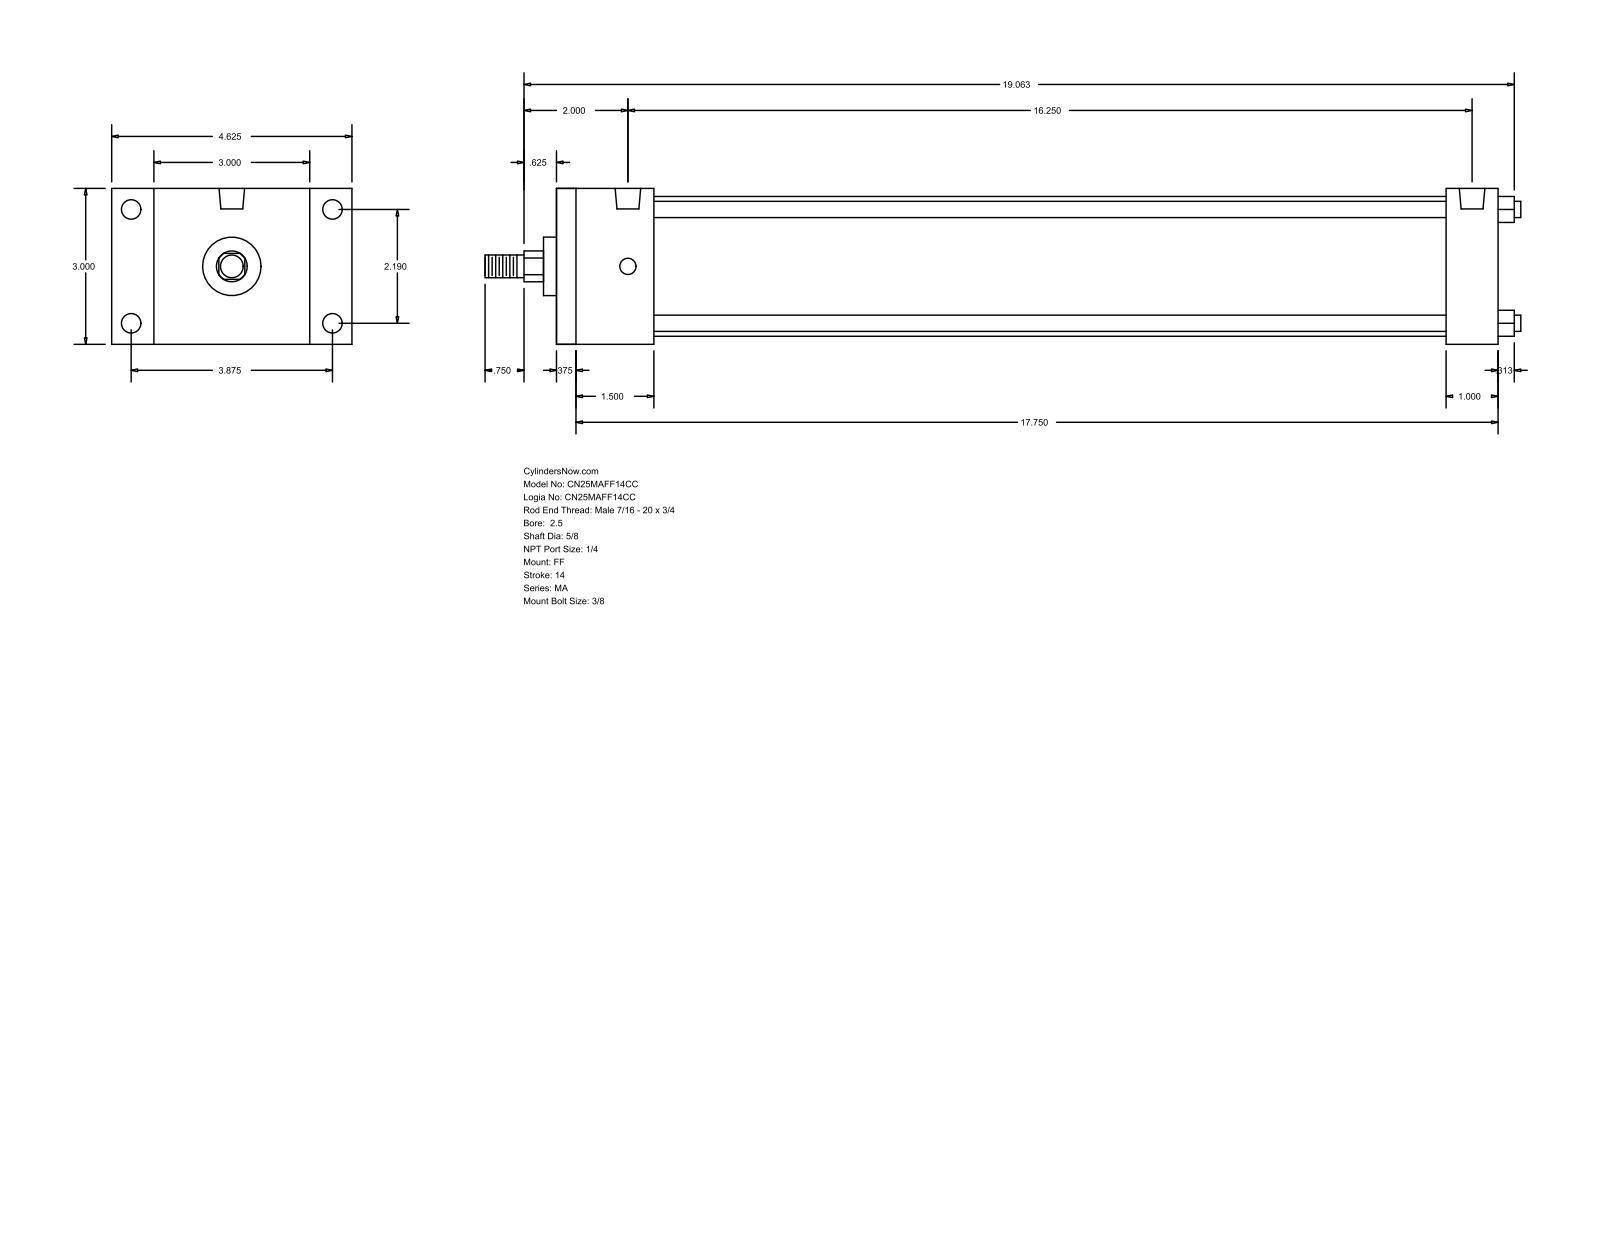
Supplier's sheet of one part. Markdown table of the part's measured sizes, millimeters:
| quantity | value |
| --- | --- |
| part name | MA_FF__0250_0.625 |
| STEP written by | GSSL Pune (CONFIG_CONTROL_DESIGN) |
| units | millimeters |
| bodies | 0 solids, 92 faces (64 planar, 28 cylindrical, 0 other) |
| overall size | 506.41 × 117.47 × 76.2 |
| round holes (diameter × count) | 7.94 × 4, 9.53 × 4, 12.49 × 2 |
| round bosses / shafts (diameter × count) | 7.94 × 4, 68.33 × 1, 28.57 × 1, 15.88 × 1, 11.11 × 1 |
| partial cylindrical surfaces (radius × count) | 7.54 × 1 |
| main face-to-face distances | 76.2, 460.37, 450.85, 9.52, 25.4, 47.62, 434.97, 38.1, 425.45, 387.35 |
| hole center spacings | 55.62, 98.42, 113.05, 412.75 |
